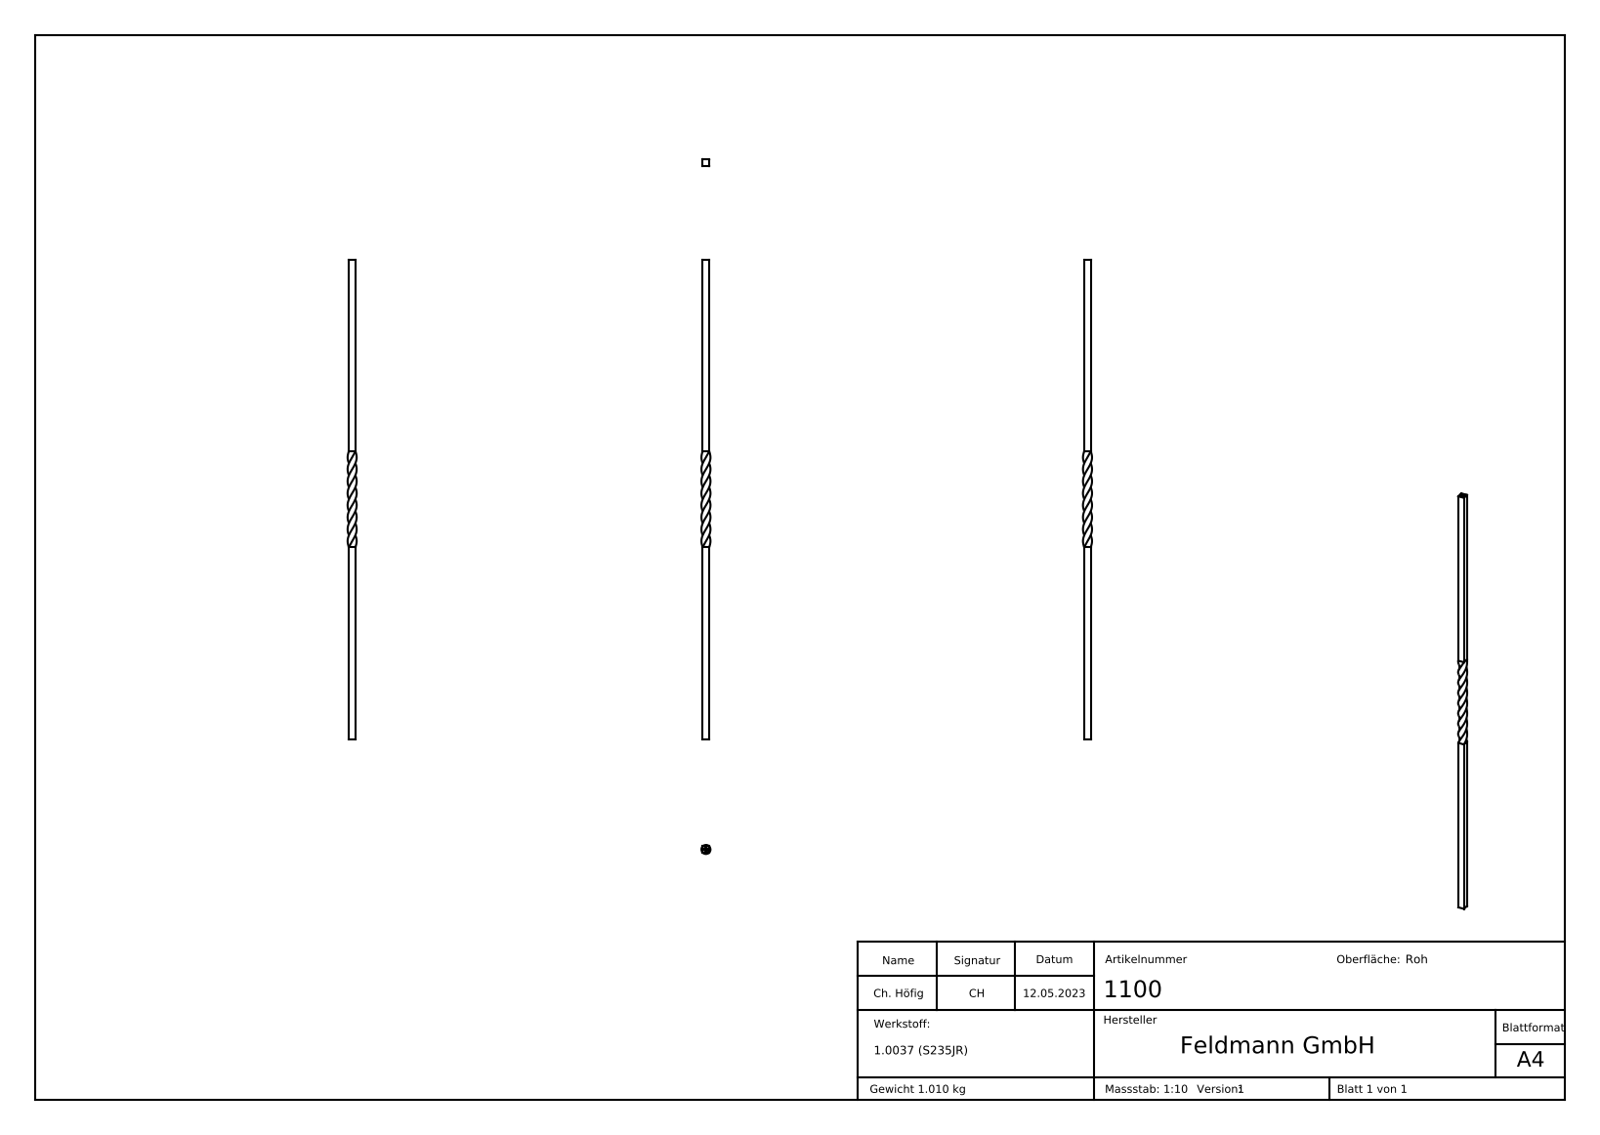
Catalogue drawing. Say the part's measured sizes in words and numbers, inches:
The part is named "1100". Its 3-D file was written by "SolidWorks 2018 (CONFIG_CONTROL_DESIGN)". It is 1 solid with 206 faces: 116 planar, 0 cylindrical and 90 other. Overall it measures 35.433 by 0.67 by 0.67 inches. Its volume is 7.906 cubic inches and its surface area 67.79 square inches. The main face-to-face distances are 0.472, 35.433, 35.429, 0.022, 0.018, 0.027, 0.045, 0.045, 0.106, 0.072.
